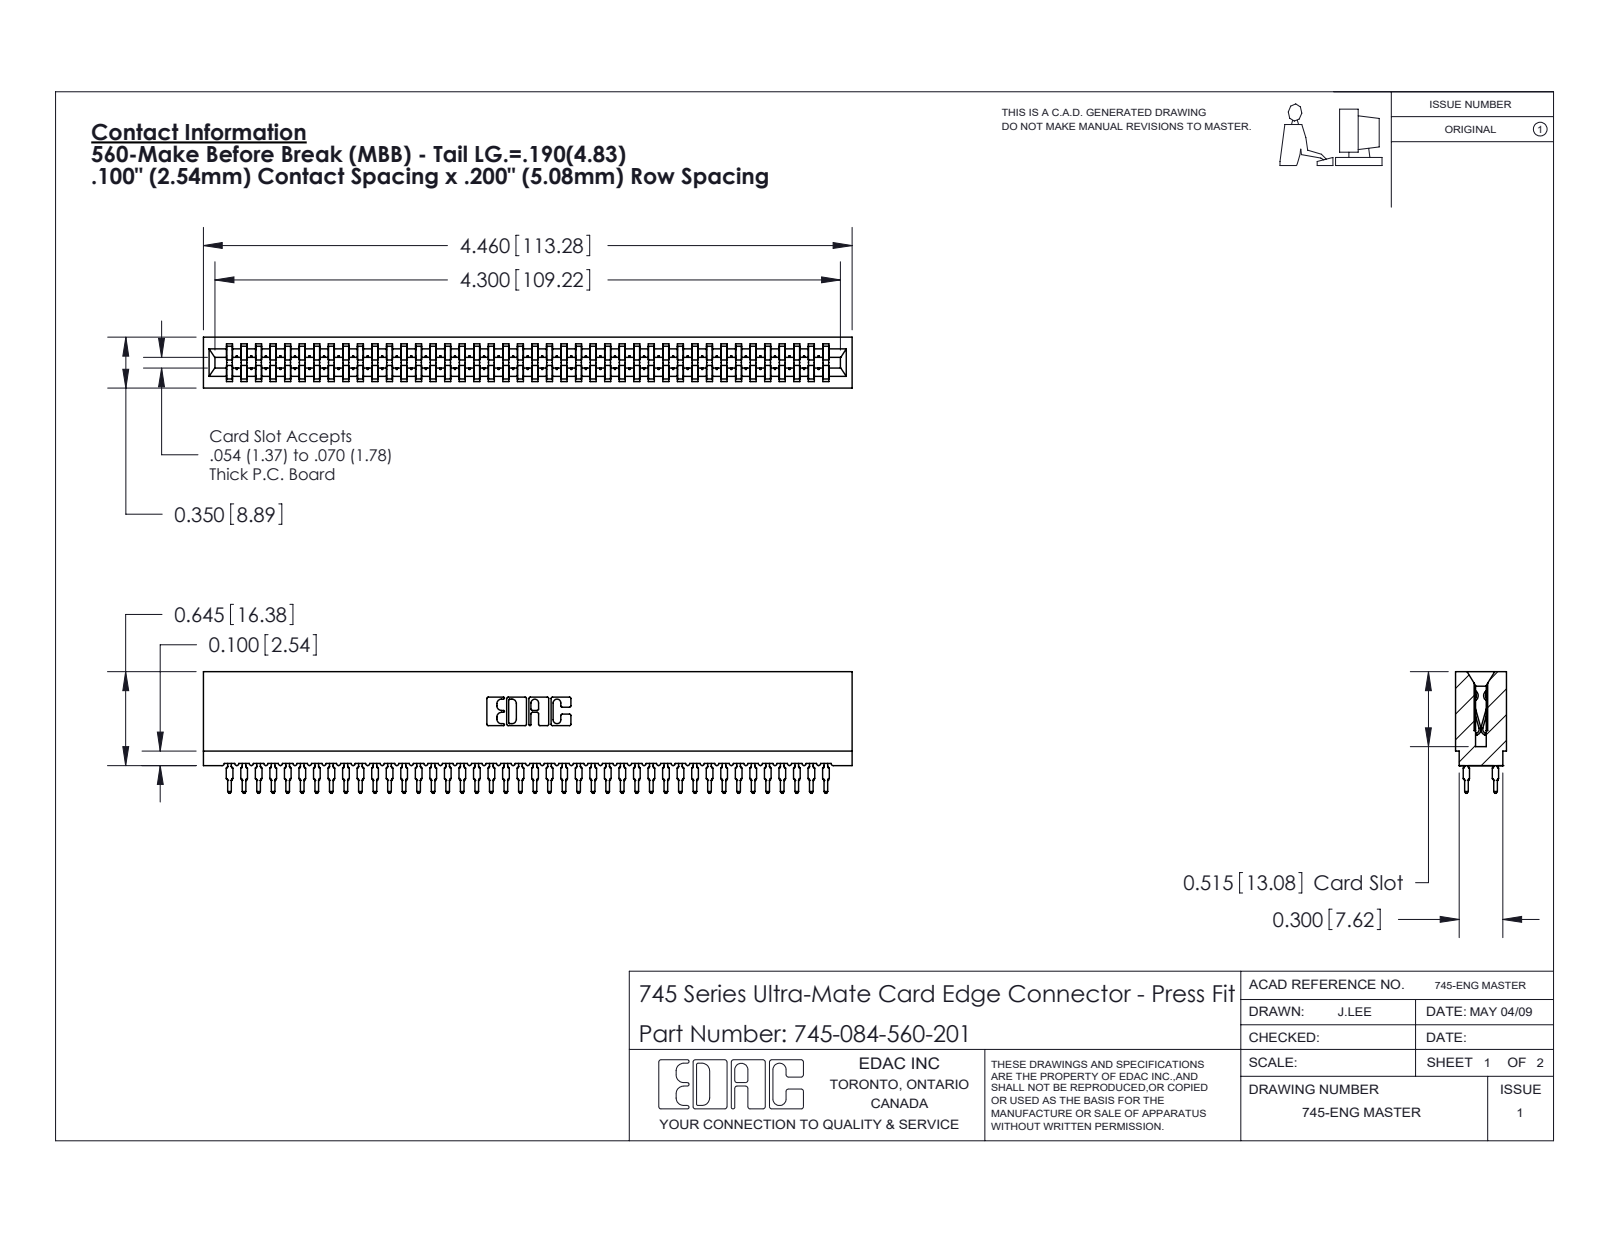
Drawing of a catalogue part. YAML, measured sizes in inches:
part_name: "745 Part_Insulator Option - 01; 745-084-560-201; 745-292-001_560"
step_written_by: "SolidWorks 2020 (CONFIG_CONTROL_DESIGN)"
units: inches
bodies: {solids: 85, faces: 8369, planar: 4339, cylindrical: 1846, other: 2184}
overall_size: [4.46, 0.836, 0.35]
volume: 0.642
surface_area: 35.18
partial_cylinders:
  - {radius: 0.021, count: 168}
  - {radius: 0.015, count: 84}
  - {radius: 0.01, count: 22}
  - {radius: 0.005, count: 8}
  - {radius: 0.011, count: 8}
  - {radius: 0.007, count: 6}
  - {radius: 0.031, count: 6}
  - {radius: 0.026, count: 3}
face_to_face_distances: [0.35, 0.2, 0.063, 0.287, 0.138, 0.212, 0.076, 0.149, 0.045, 0.305]
